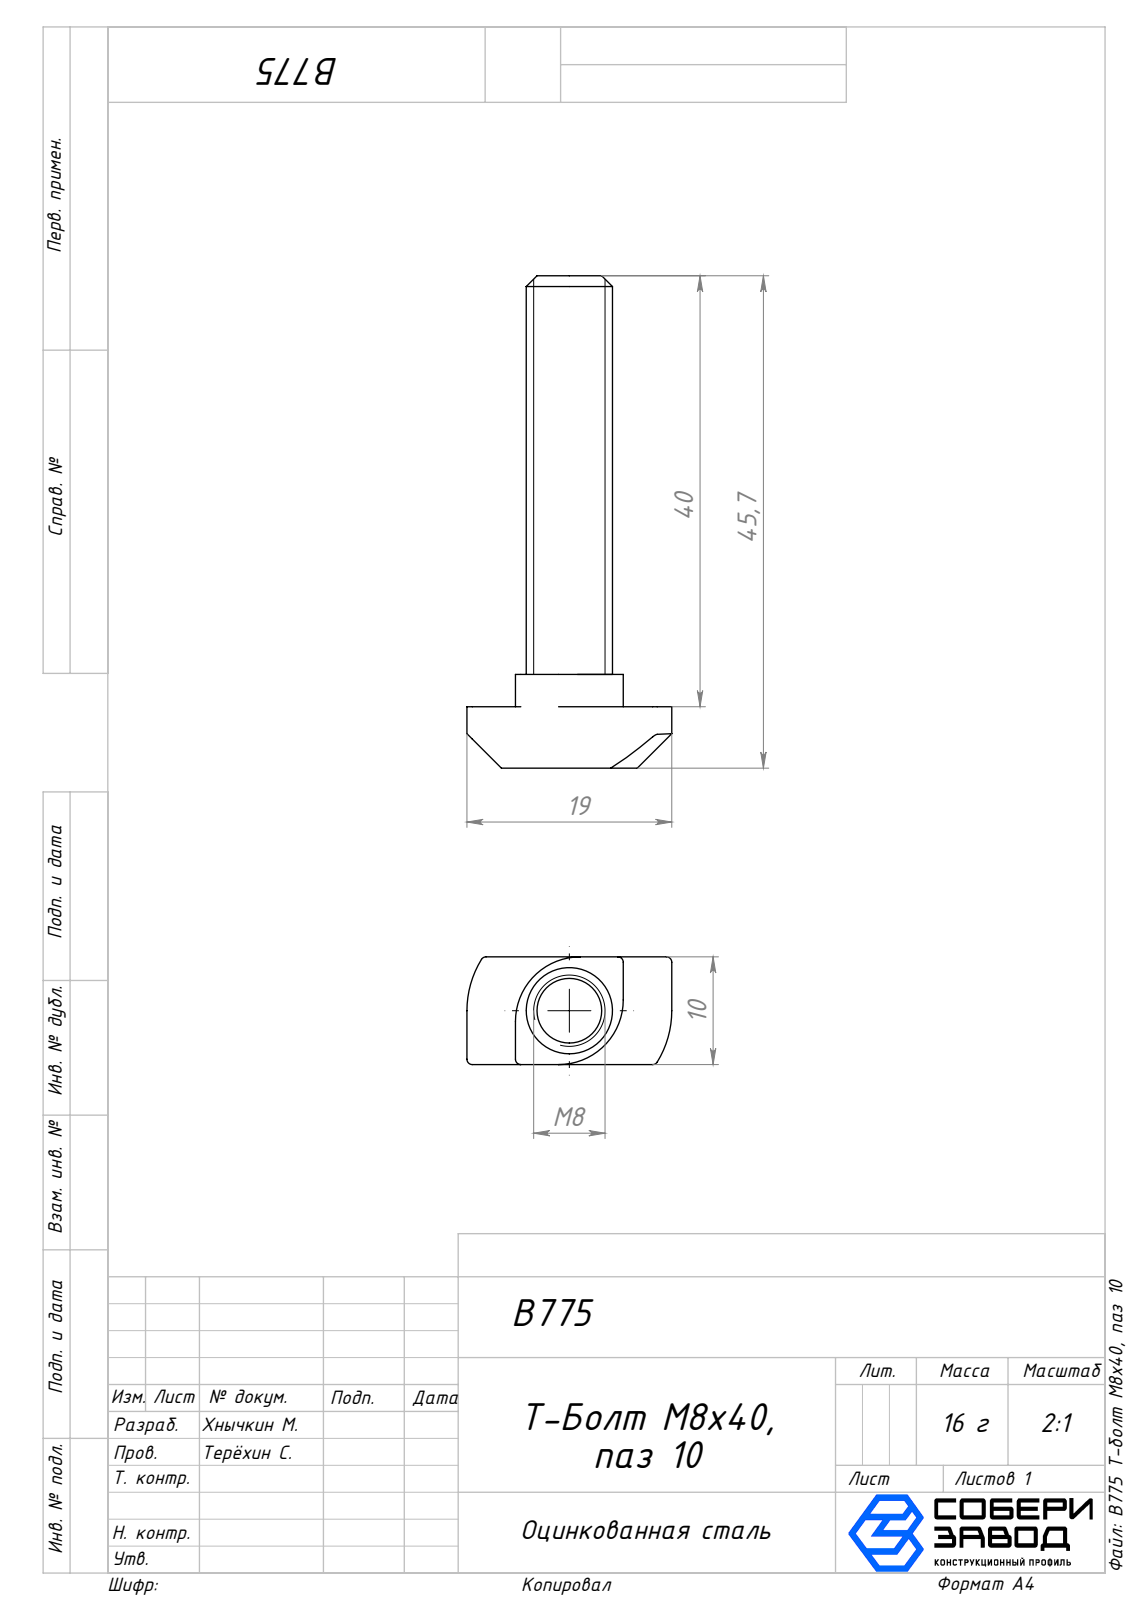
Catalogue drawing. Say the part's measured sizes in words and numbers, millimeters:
The part is named "B775 Т-болт М8х40, паз 10". Its 3-D file was written by "SolidWorks 2025 (AUTOMOTIVE_DESIGN)". It is 1 solid with 29 faces: 13 planar, 12 cylindrical and 4 other. Overall it measures 45.7 by 19 by 10 millimeters. Its volume is 3 051 cubic millimeters and its surface area 1 642 square millimeters. Round bosses or shafts: 1 of diameter 8. Partial cylindrical surfaces (rounded edges, fillets, slot ends): 6 of radius 0.5, 2 of radius 6, 2 of radius 9.08. The main face-to-face distances are 10, 5.7, 8.7, 3, 45.7, 40, 37, 4.5, 14.5, 19.
